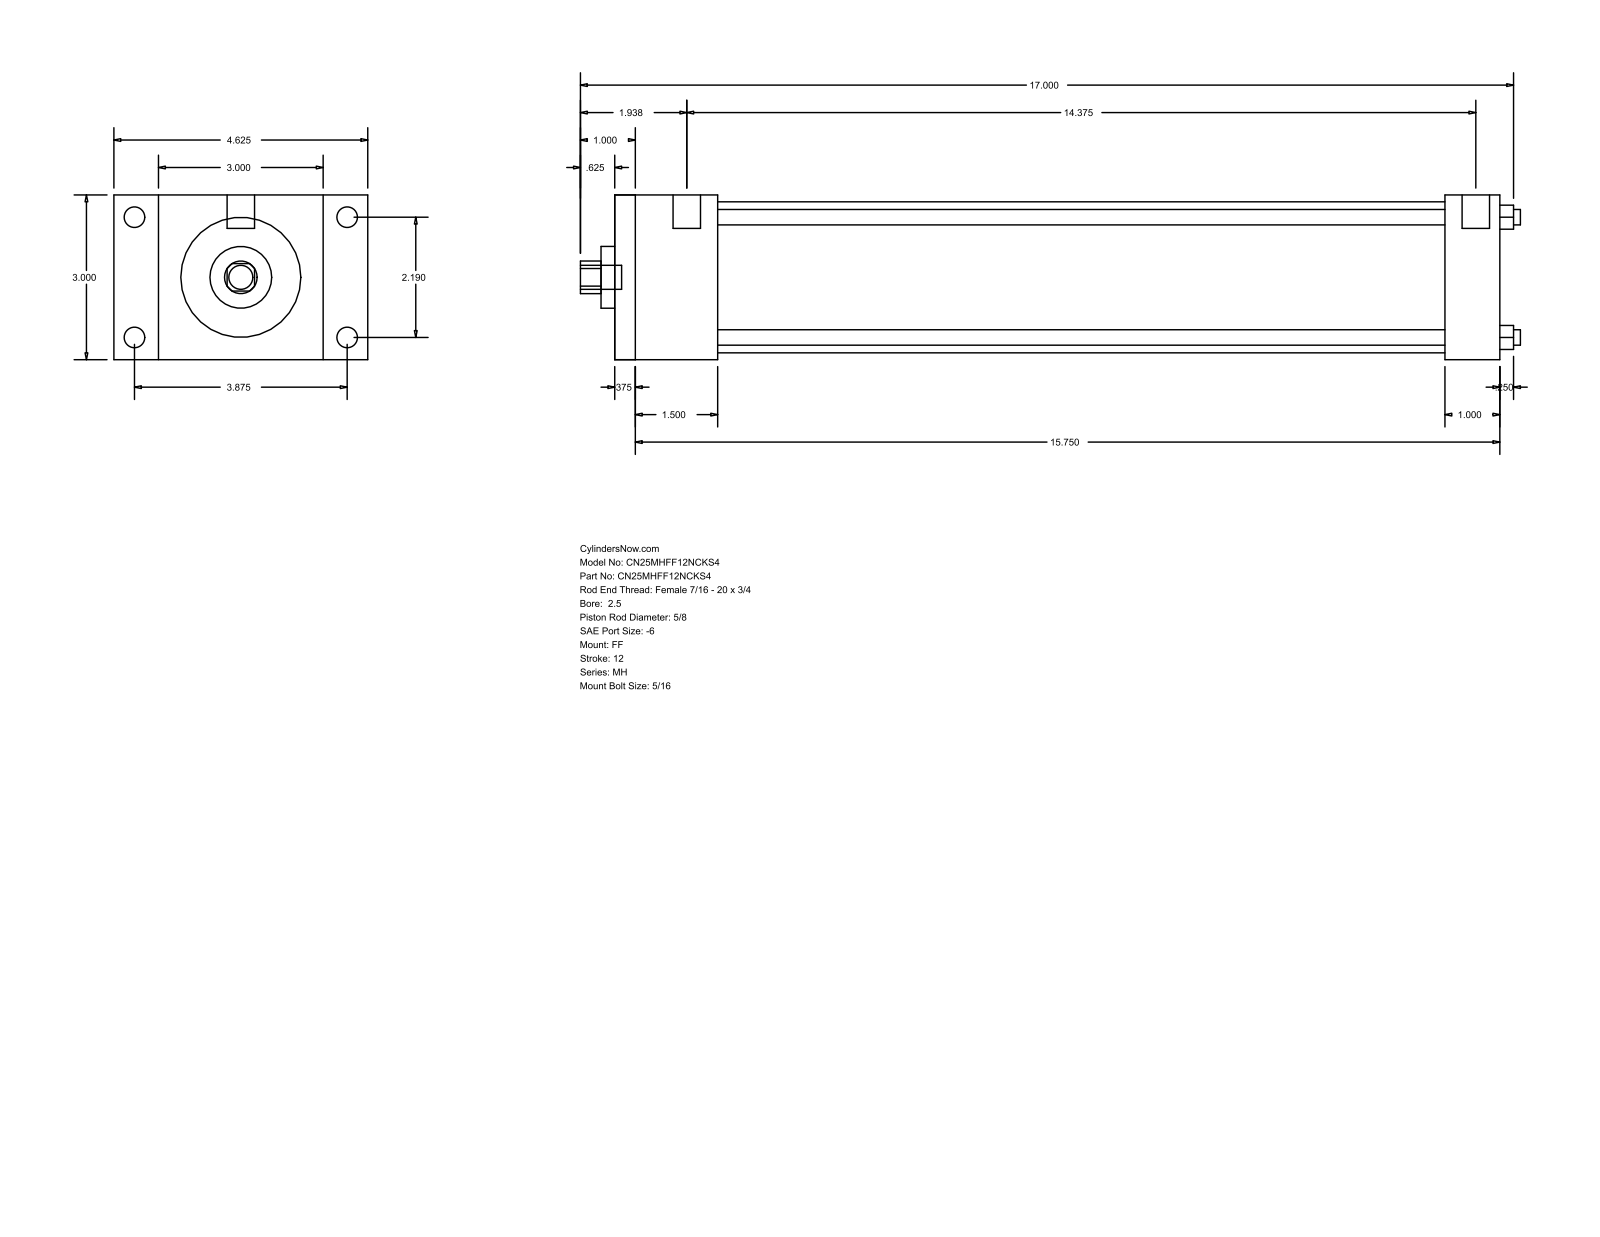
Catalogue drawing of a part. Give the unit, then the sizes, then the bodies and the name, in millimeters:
Units: millimetres
Overall size (bounding box): 434.98 × 117.47 × 76.2
Round holes (diameter × count): ⌀7.14 ×4, ⌀15.88 ×1, ⌀28.57 ×1, ⌀69.85 ×1
Round bosses / shafts (diameter × count): ⌀9.53 ×4, ⌀5.56 ×4, ⌀12.7 ×2, ⌀11.11 ×1
Partial cylindrical surfaces — rounded edges, fillets, slot ends (radius × count): R7.54 ×1
Main face-to-face distances: 76.2, 409.57, 9.52, 400.05, 25.4, 47.62, 384.17, 38.1, 374.65, 336.55
Hole centre spacings: 39.33, 55.62, 78.66
Bodies: 0 solids, 92 faces (64 planar, 28 cylindrical, 0 other)
Part name (STEP PRODUCT): MH_FF__0250_0.625
STEP written by: GSSL Pune (CONFIG_CONTROL_DESIGN)
